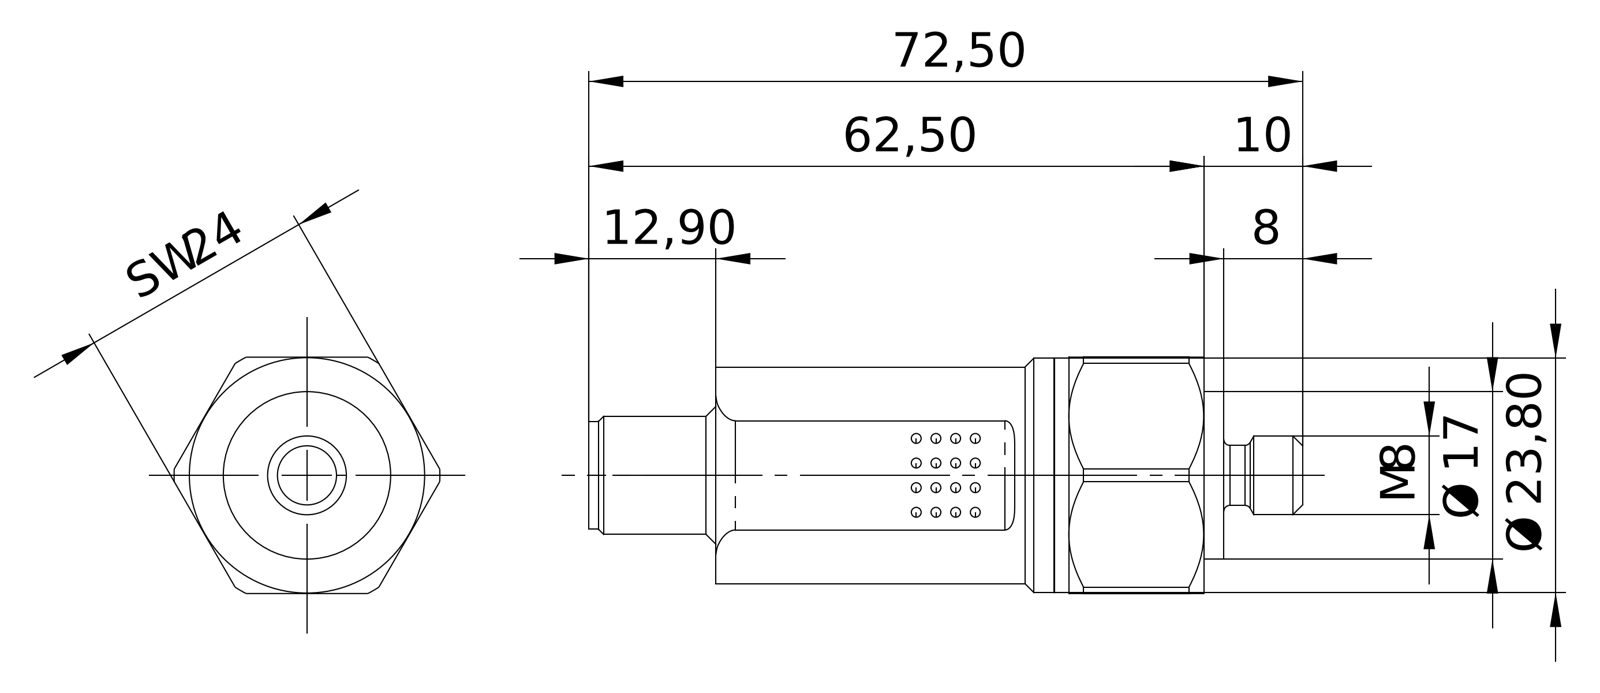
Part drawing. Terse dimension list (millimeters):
name: 02.118.004
written by: SolidWorks 2020 (AUTOMOTIVE_DESIGN)
unit: mm
bodies: 1 solid, 261 faces (178 planar, 25 cylindrical, 58 other)
size: 72.5 × 27 × 24
volume: 21 762 mm³; area: 5 561 mm²
holes: 1× ⌀8.38, 1× ⌀8.4
bosses: 4× ⌀1, 1× ⌀23.8, 1× ⌀22, 1× ⌀17, 1× ⌀12, 1× ⌀10.9, 1× ⌀8, 1× ⌀6.1
rounds: 2× R1, 2× R2, 1× R0.57, 1× R13.5
face distances: 24, 19, 2, 51.6, 49.6, 55.85, 53.85, 4.25, 64.5, 62.5
